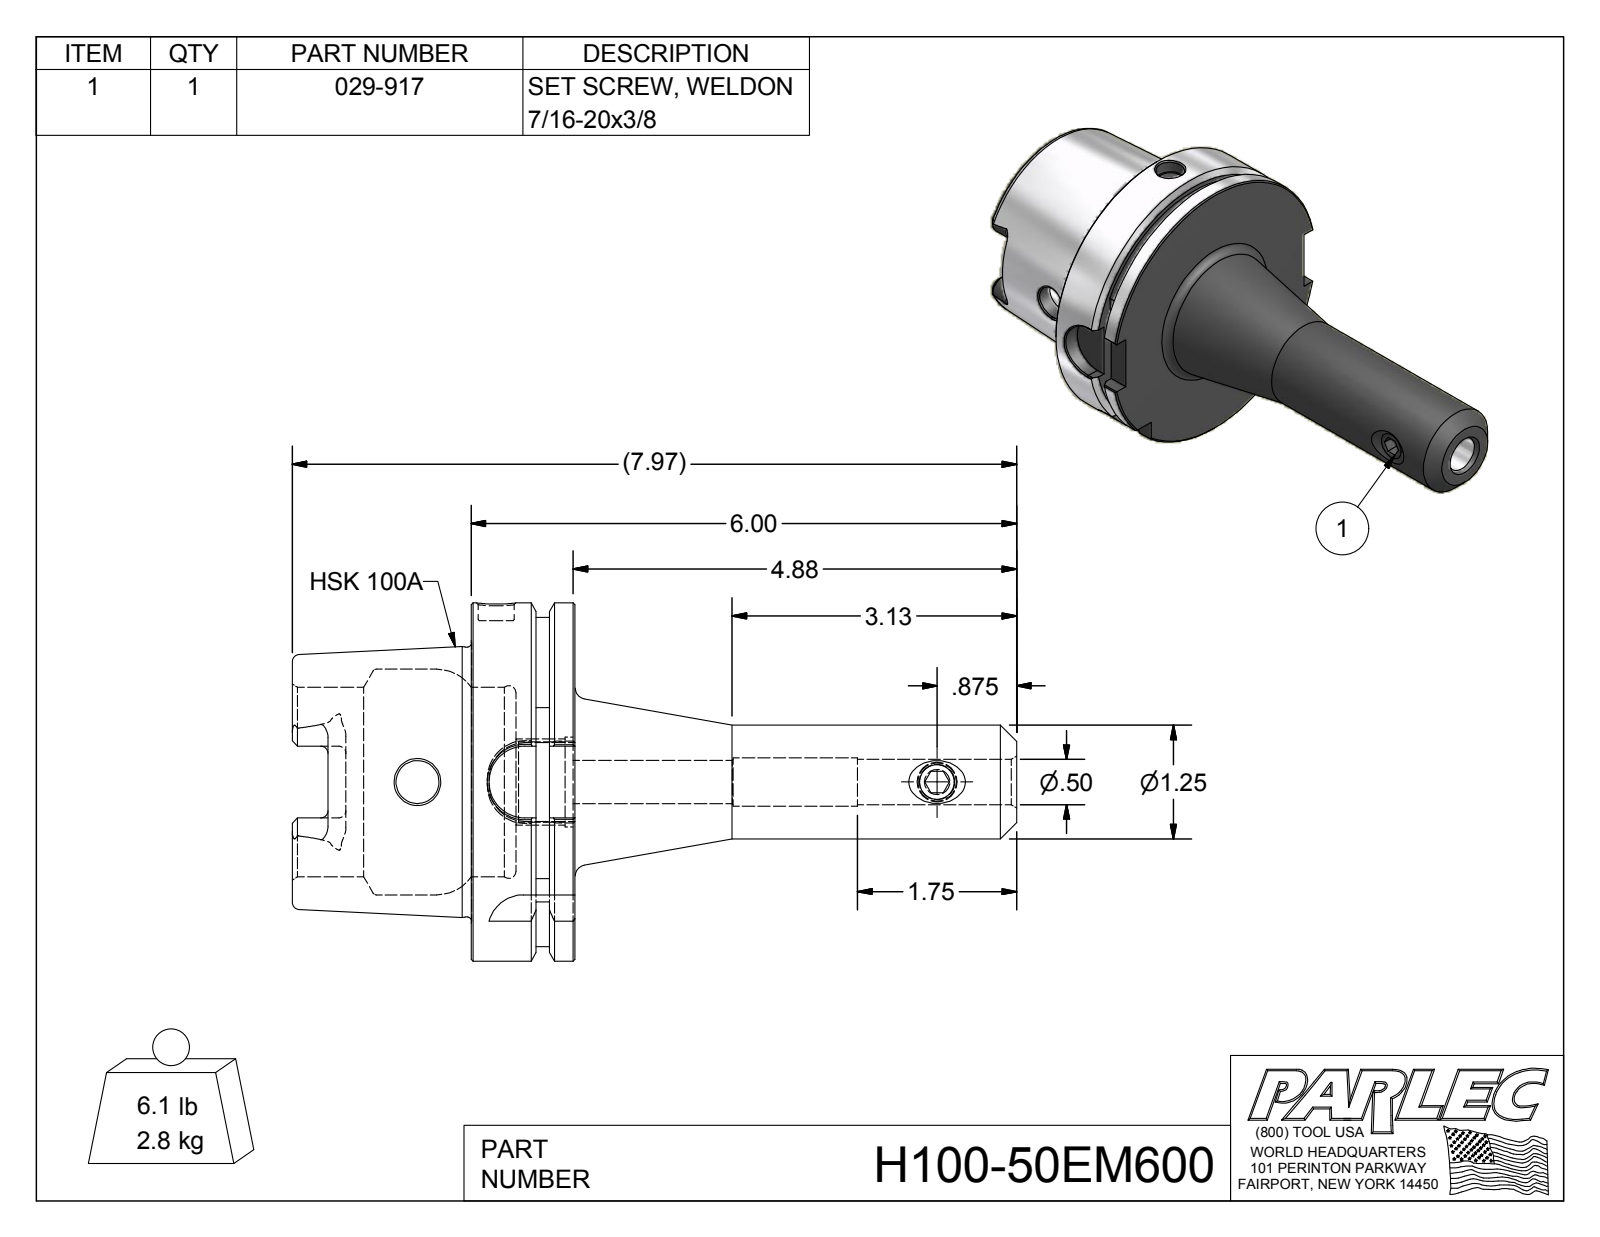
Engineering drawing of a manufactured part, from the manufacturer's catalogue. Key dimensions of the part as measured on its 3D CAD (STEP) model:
Part name (STEP PRODUCT): H100-50EM600; 029-917
STEP written by: Autodesk Inventor 2012 (AUTOMOTIVE_DESIGN)
Units: inches
Bodies: 2 solids, 141 faces (53 planar, 36 cylindrical, 52 other)
Overall size (bounding box): 7.969 × 3.937 × 3.937
Volume: 21.64 in³ · Surface area: 104.8 in²
Round holes (diameter × count): ⌀0.472 ×2, ⌀0.383 ×1, ⌀0.394 ×1, ⌀0.5 ×1, ⌀0.53 ×1, ⌀0.881 ×1, ⌀0.985 ×1, ⌀2.087 ×1, ⌀2.48 ×1
Round bosses / shafts (diameter × count): ⌀3.937 ×1, ⌀2.967 ×1, ⌀1.25 ×1, ⌀0.437 ×1
Partial cylindrical surfaces — rounded edges, fillets, slot ends (radius × count): R0.079 ×6, R0.192 ×4, R0.394 ×4, R1.811 ×1
Main face-to-face distances: 1.142, 0.492, 0.65, 1.969, 2.461, 3.11, 2.83, 0.861, 0.369, 0.28
Hole centre spacings: 5.716
